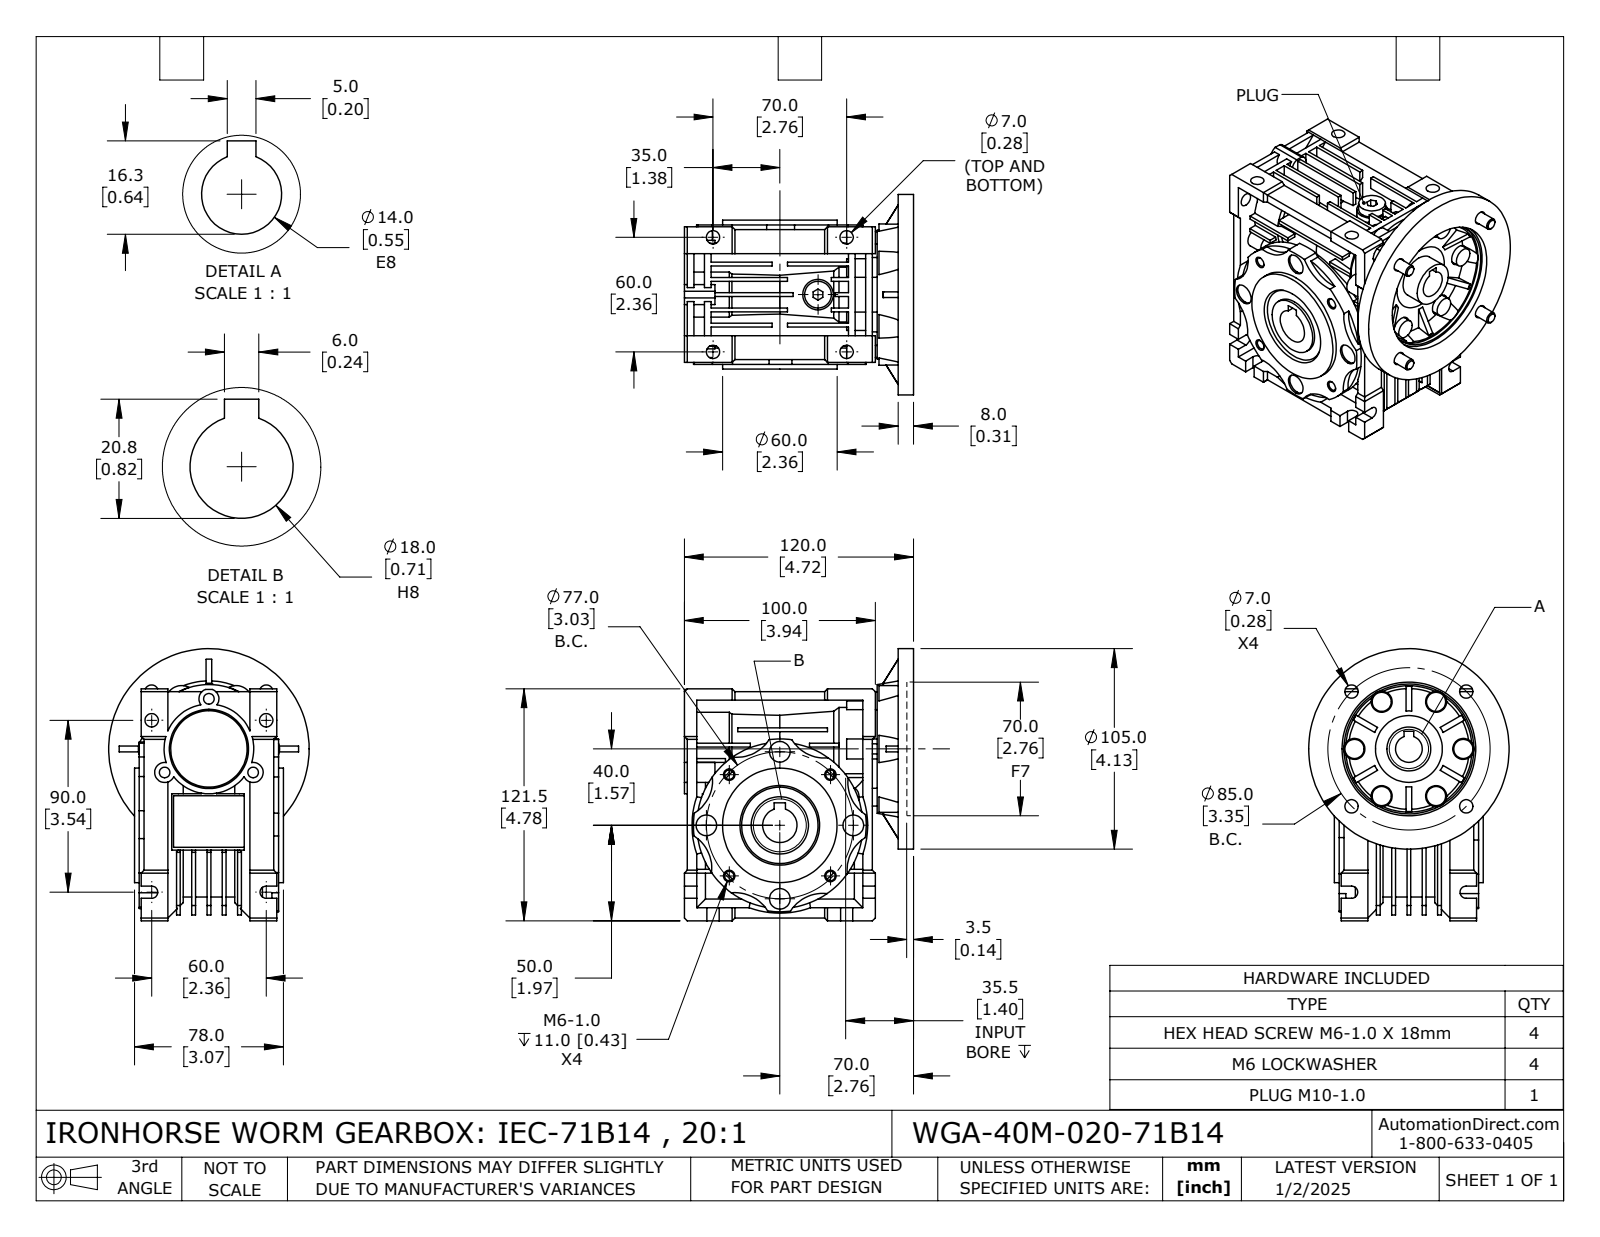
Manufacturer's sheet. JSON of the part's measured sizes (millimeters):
{"part_name": "WGA-40M-020-71B14", "step_written_by": "SolidWorks 2024 (CONFIG_CONTROL_DESIGN)", "units": "millimeters", "bodies": {"solids": 14, "faces": 956, "planar": 550, "cylindrical": 281, "other": 125}, "overall_size": [142.5, 128.5, 105], "volume_mm3": 688964, "surface_area_mm2": 170588, "round_holes": [[7, 10], [11, 6], [4.92, 4], [6.1, 4], [10.8, 4], [5.55, 3], [9, 1], [14, 1], [15, 1], [18, 1], [23, 1], [28, 1]], "round_bosses_or_shafts": [[10, 6], [12.2, 4], [6, 4], [105, 1], [75, 1], [60, 1], [54, 1], [47, 1]], "partial_cylinders_radius": [[20, 8], [3.2, 6], [5.22, 6], [8.5, 6], [5.25, 3], [34.31, 1], [43.5, 1], [43.59, 1]], "face_to_face_distances": [8, 6, 2, 1.5, 16, 10, 5, 11, 2.5, 24], "hole_center_spacings": [28.5, 29.1, 70.22, 49.36, 16.69, 30.09, 33.54, 37.5]}
